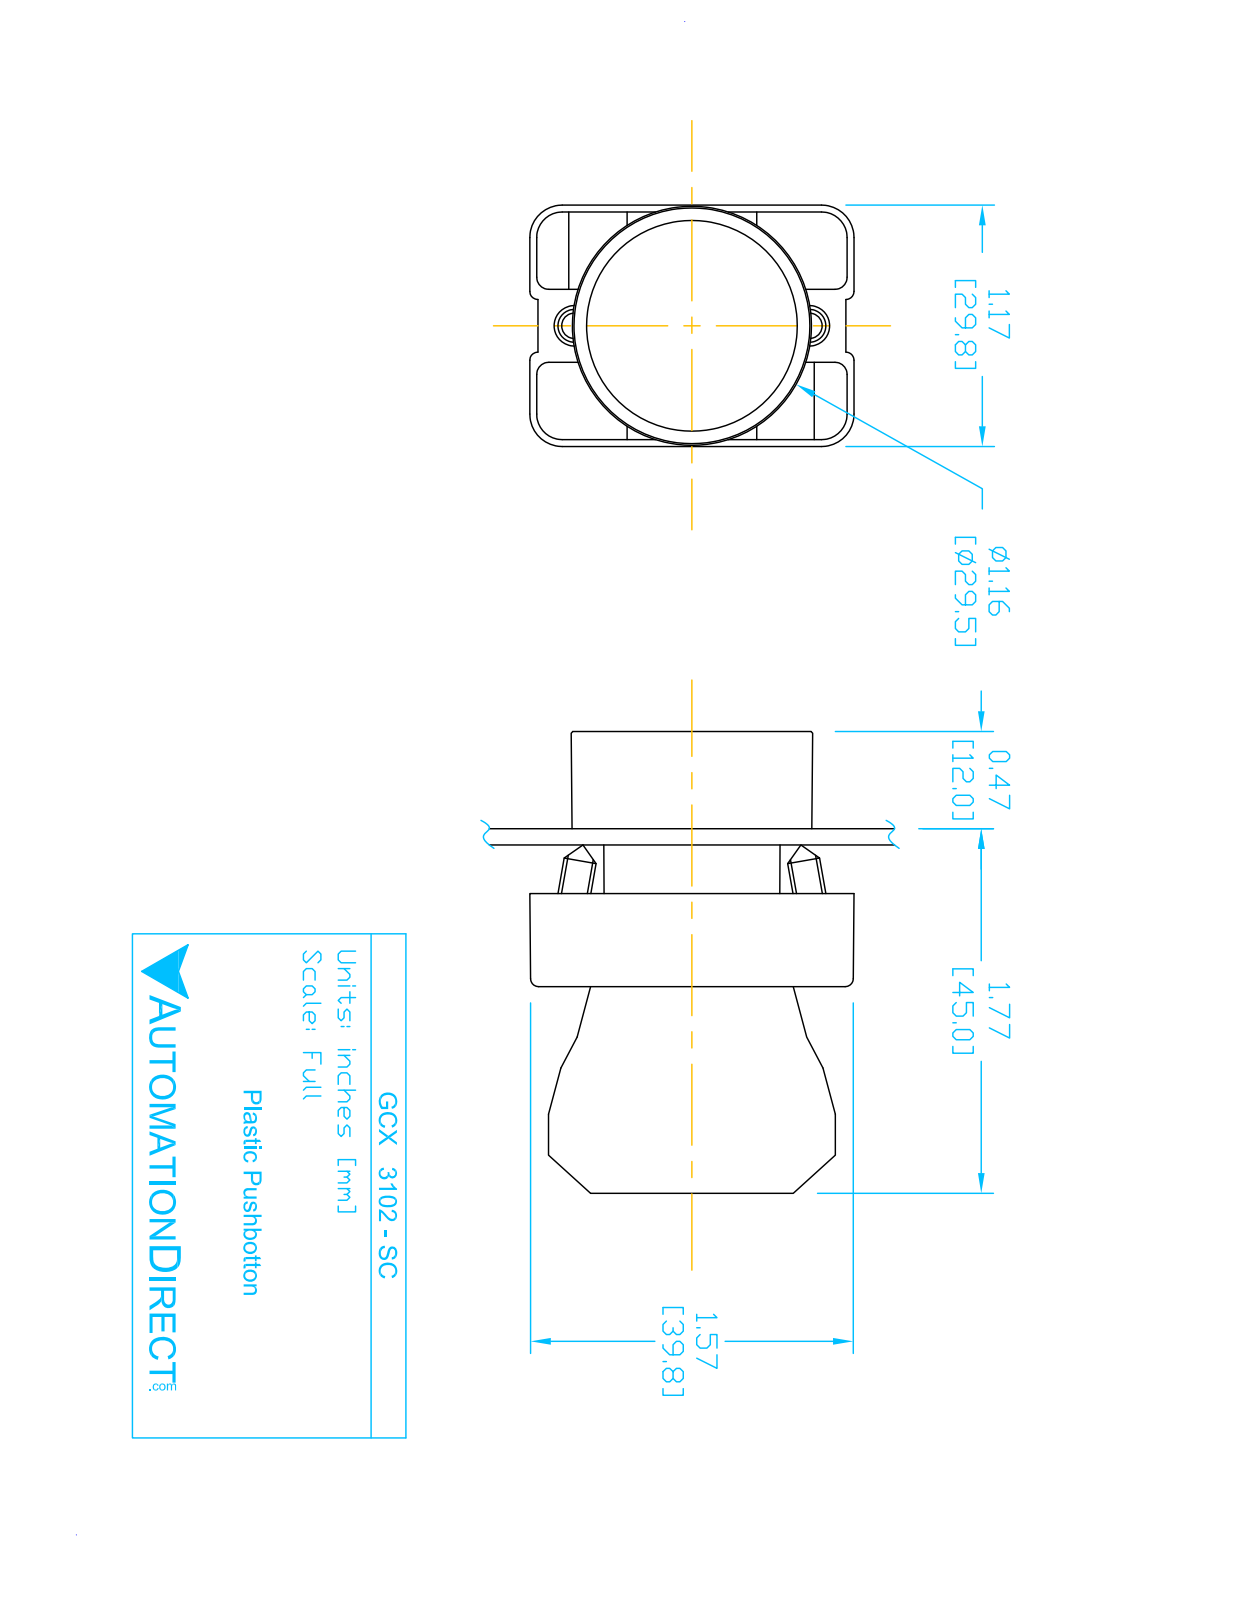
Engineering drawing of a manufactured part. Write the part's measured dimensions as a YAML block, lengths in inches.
part_name: "ECX3029-2; GCX3102 OPERATOR; GCX3102-SC"
step_written_by: "SolidWorks 2016 (AUTOMOTIVE_DESIGN)"
units: inches
bodies: {solids: 5, faces: 288, planar: 147, cylindrical: 118, other: 23}
overall_size: [1.581, 1.407, 1.177]
volume: 1.09
surface_area: 20.41
round_holes:
  - {diameter: 0.124, count: 2}
  - {diameter: 0.13, count: 2}
  - {diameter: 0.197, count: 1}
  - {diameter: 0.878, count: 1}
  - {diameter: 0.888, count: 1}
  - {diameter: 1.024, count: 1}
round_bosses_or_shafts:
  - {diameter: 0.157, count: 2}
  - {diameter: 1.175, count: 1}
  - {diameter: 1.004, count: 1}
  - {diameter: 0.945, count: 1}
  - {diameter: 0.856, count: 1}
  - {diameter: 0.78, count: 1}
partial_cylinders:
  - {radius: 0.059, count: 24}
  - {radius: 0.041, count: 12}
  - {radius: 0.124, count: 12}
  - {radius: 0.157, count: 12}
  - {radius: 0.039, count: 4}
  - {radius: 0.128, count: 2}
  - {radius: 0.392, count: 1}
  - {radius: 0.398, count: 1}
face_to_face_distances: [0.033, 0.72, 1.193, 0.472, 0.031, 0.689, 1.161, 0.122, 0.091, 0.598]
